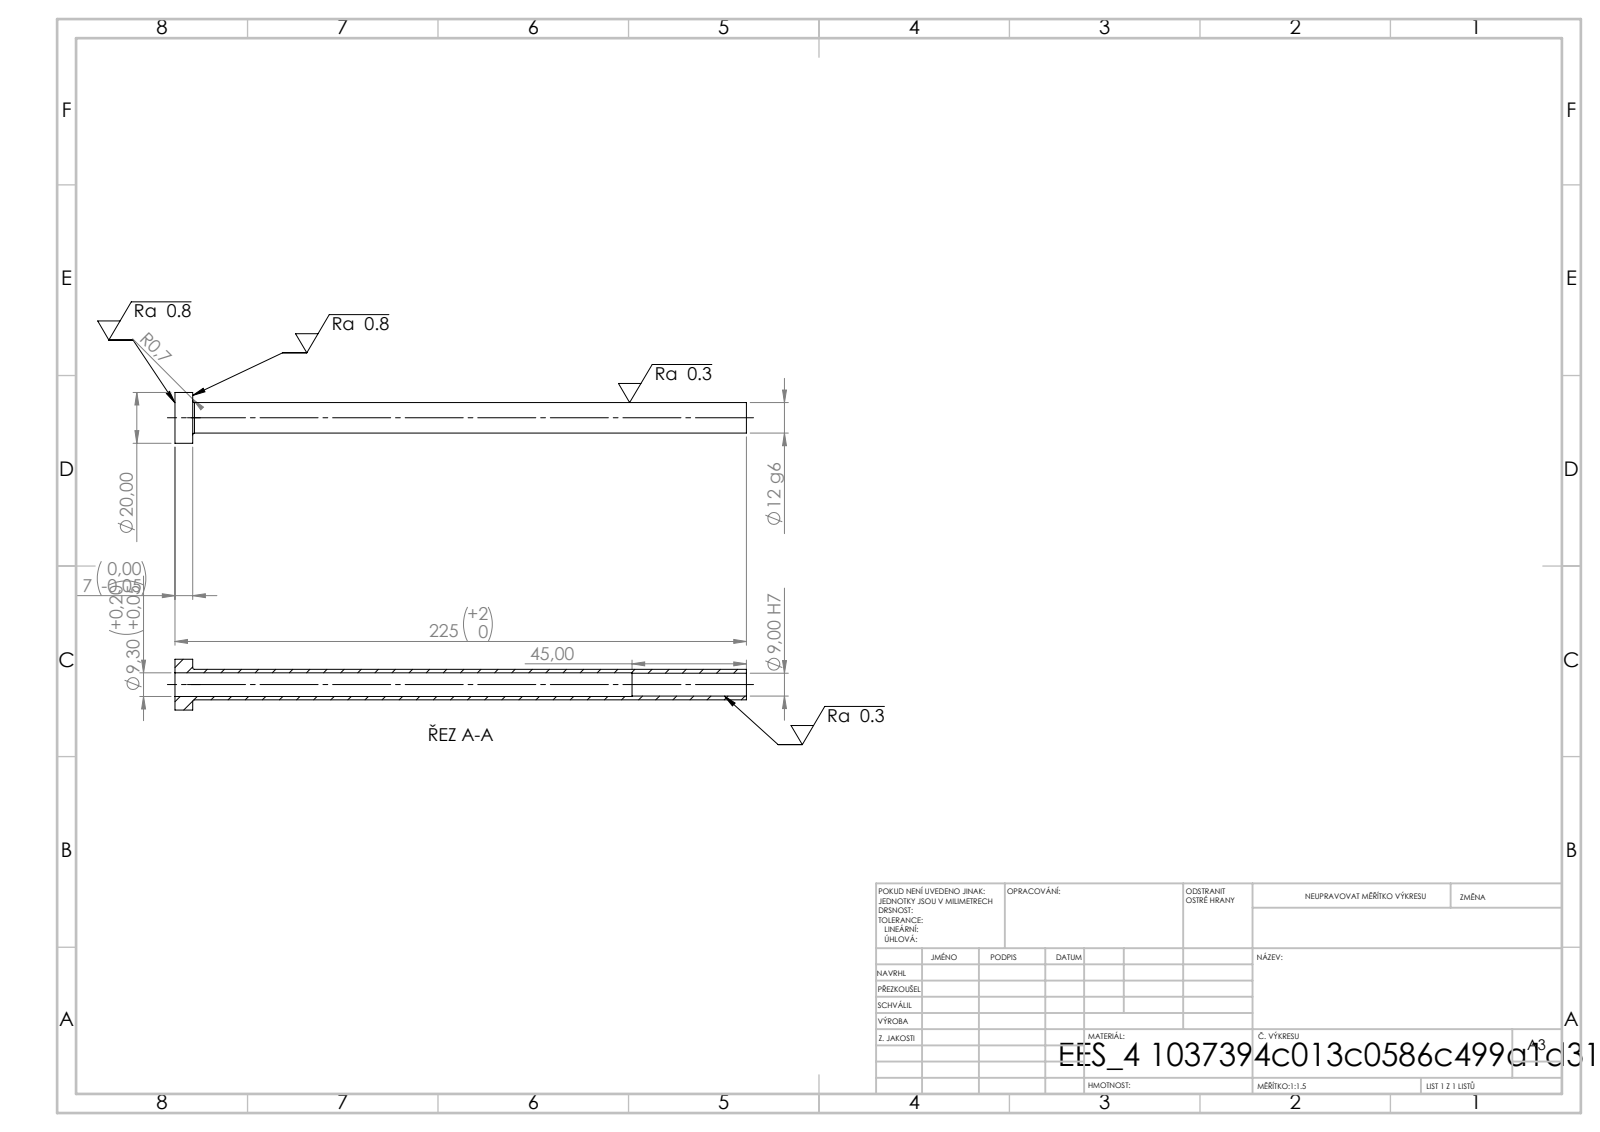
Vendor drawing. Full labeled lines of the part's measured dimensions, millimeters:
STEP written by: SolidWorks 2019 (CONFIG_CONTROL_DESIGN)
Units: millimetres
Bodies: 1 solid, 14 faces (4 planar, 8 cylindrical, 2 other)
Overall size (bounding box): 225 × 20 × 20
Volume: 11 768 mm³ · Surface area: 15 680 mm²
Round holes (diameter × count): ⌀9 ×1, ⌀9.3 ×1
Round bosses / shafts (diameter × count): ⌀20 ×1, ⌀12 ×1
Main face-to-face distances: 7, 225, 218, 180, 173, 45
